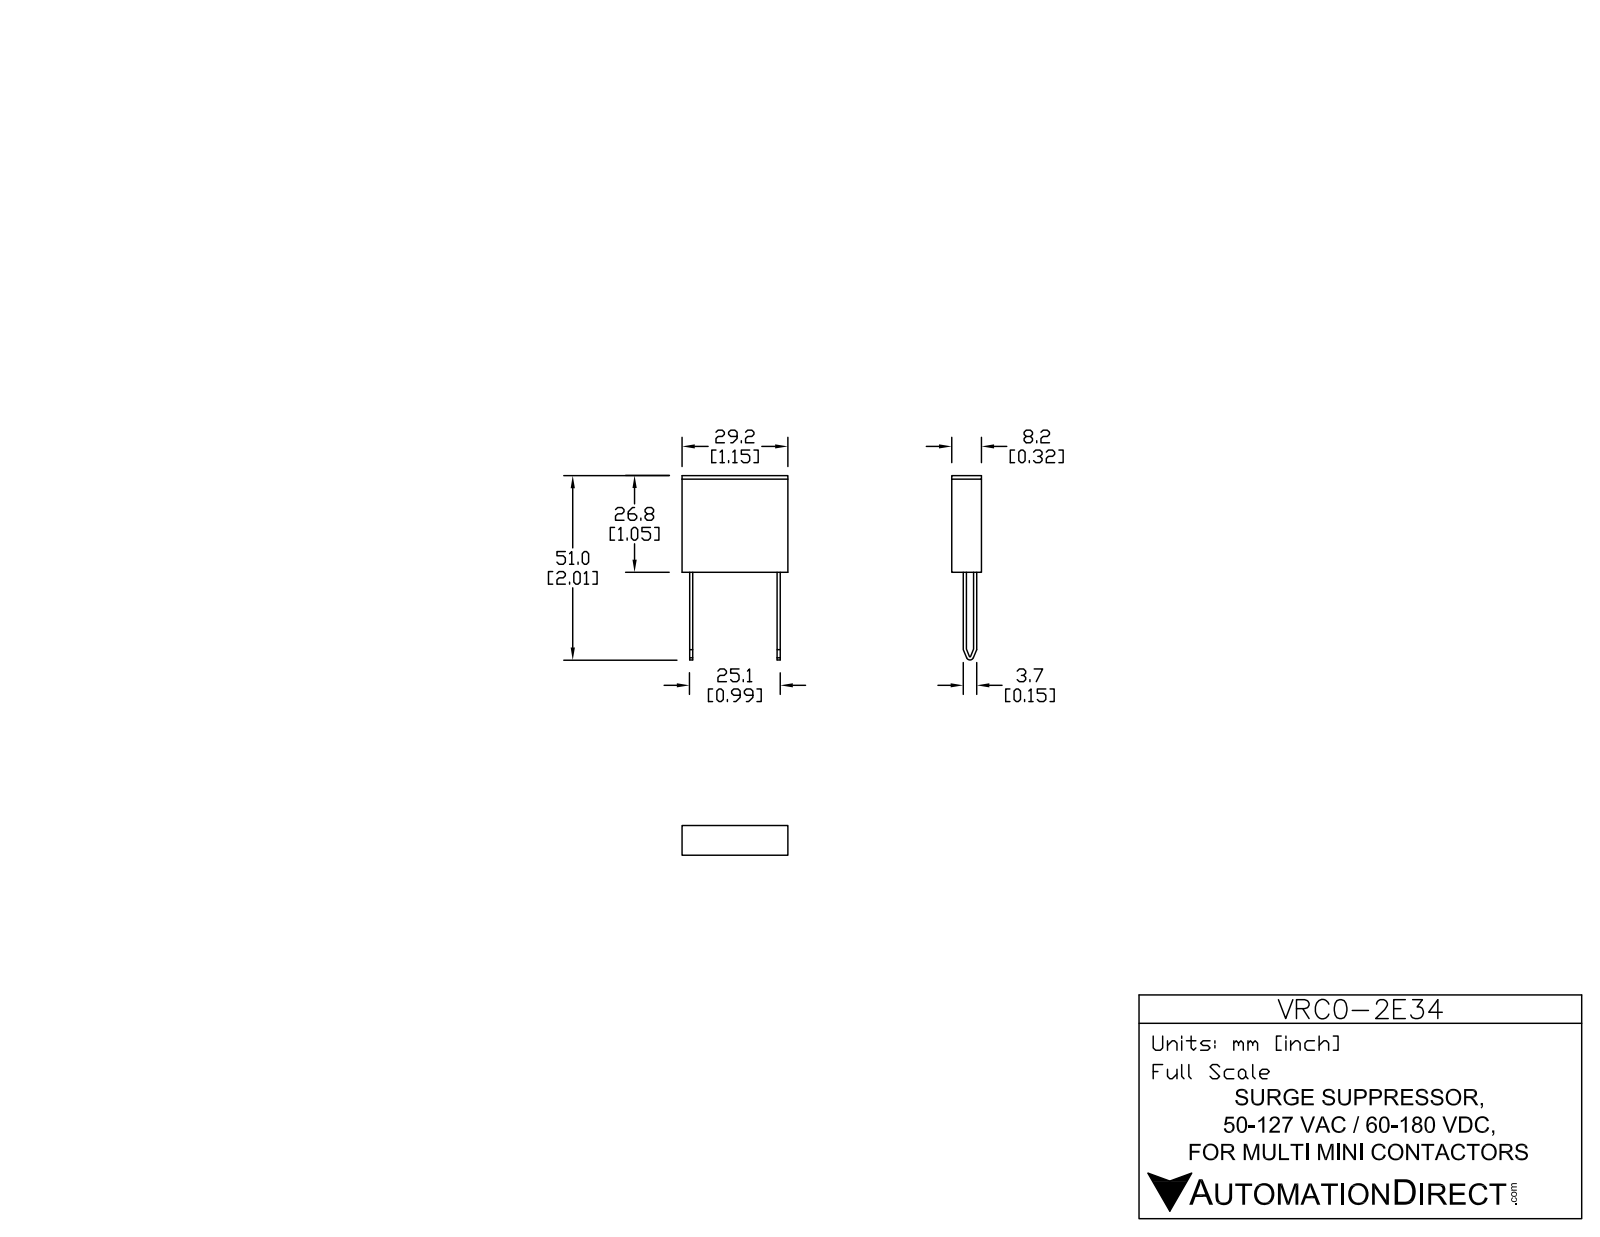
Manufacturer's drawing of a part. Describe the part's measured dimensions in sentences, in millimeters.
The part is named "VRC0-2E34". Its 3-D file was written by "SolidWorks 2013 (AUTOMOTIVE_DESIGN)". It is 1 solid with 34 faces: 26 planar, 8 cylindrical and 0 other. Overall it measures 50.9 by 29.2 by 8.2 millimeters. Its volume is 6 463 cubic millimeters and its surface area 2 803 square millimeters. Partial cylindrical surfaces (rounded edges, fillets, slot ends): 1 of radius 0.15, 1 of radius 1. The main face-to-face distances are 8.2, 26.7, 29.2, 0.85, 2.1, 27.1, 2.95, 26.25, 24.15, 2.85.
